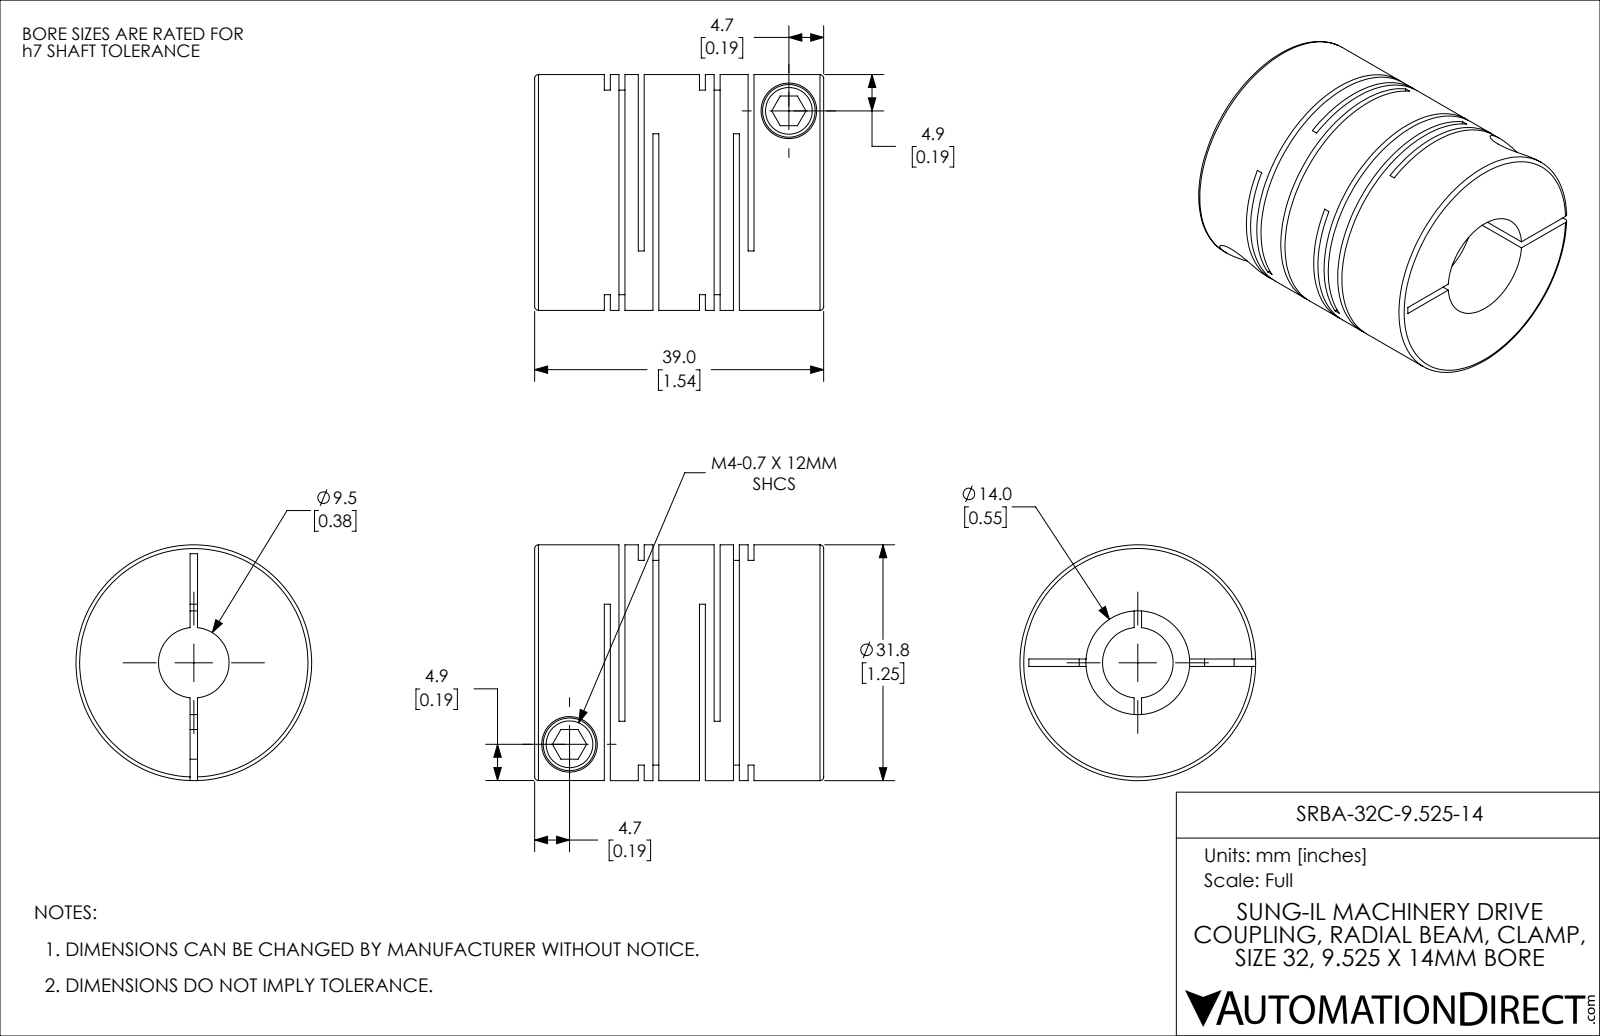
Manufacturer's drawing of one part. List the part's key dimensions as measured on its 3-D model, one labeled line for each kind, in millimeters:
Part name (STEP PRODUCT): SRBA-32C-9.525-14
STEP written by: SolidWorks 2021 (CONFIG_CONTROL_DESIGN)
Units: millimetres
Bodies: 1 solid, 114 faces (60 planar, 42 cylindrical, 12 other)
Overall size (bounding box): 39 × 31.8 × 31.8
Volume: 21 802 mm³ · Surface area: 15 234 mm²
Round holes (diameter × count): ⌀4 ×2, ⌀7.5 ×2, ⌀9.53 ×1, ⌀14 ×1
Round bosses / shafts (diameter × count): ⌀7.1 ×2, ⌀31.8 ×1
Main face-to-face distances: 0.8, 12.84, 1.98, 4.58, 12.04, 1.18, 10.86, 3.78, 8.26, 2.6
